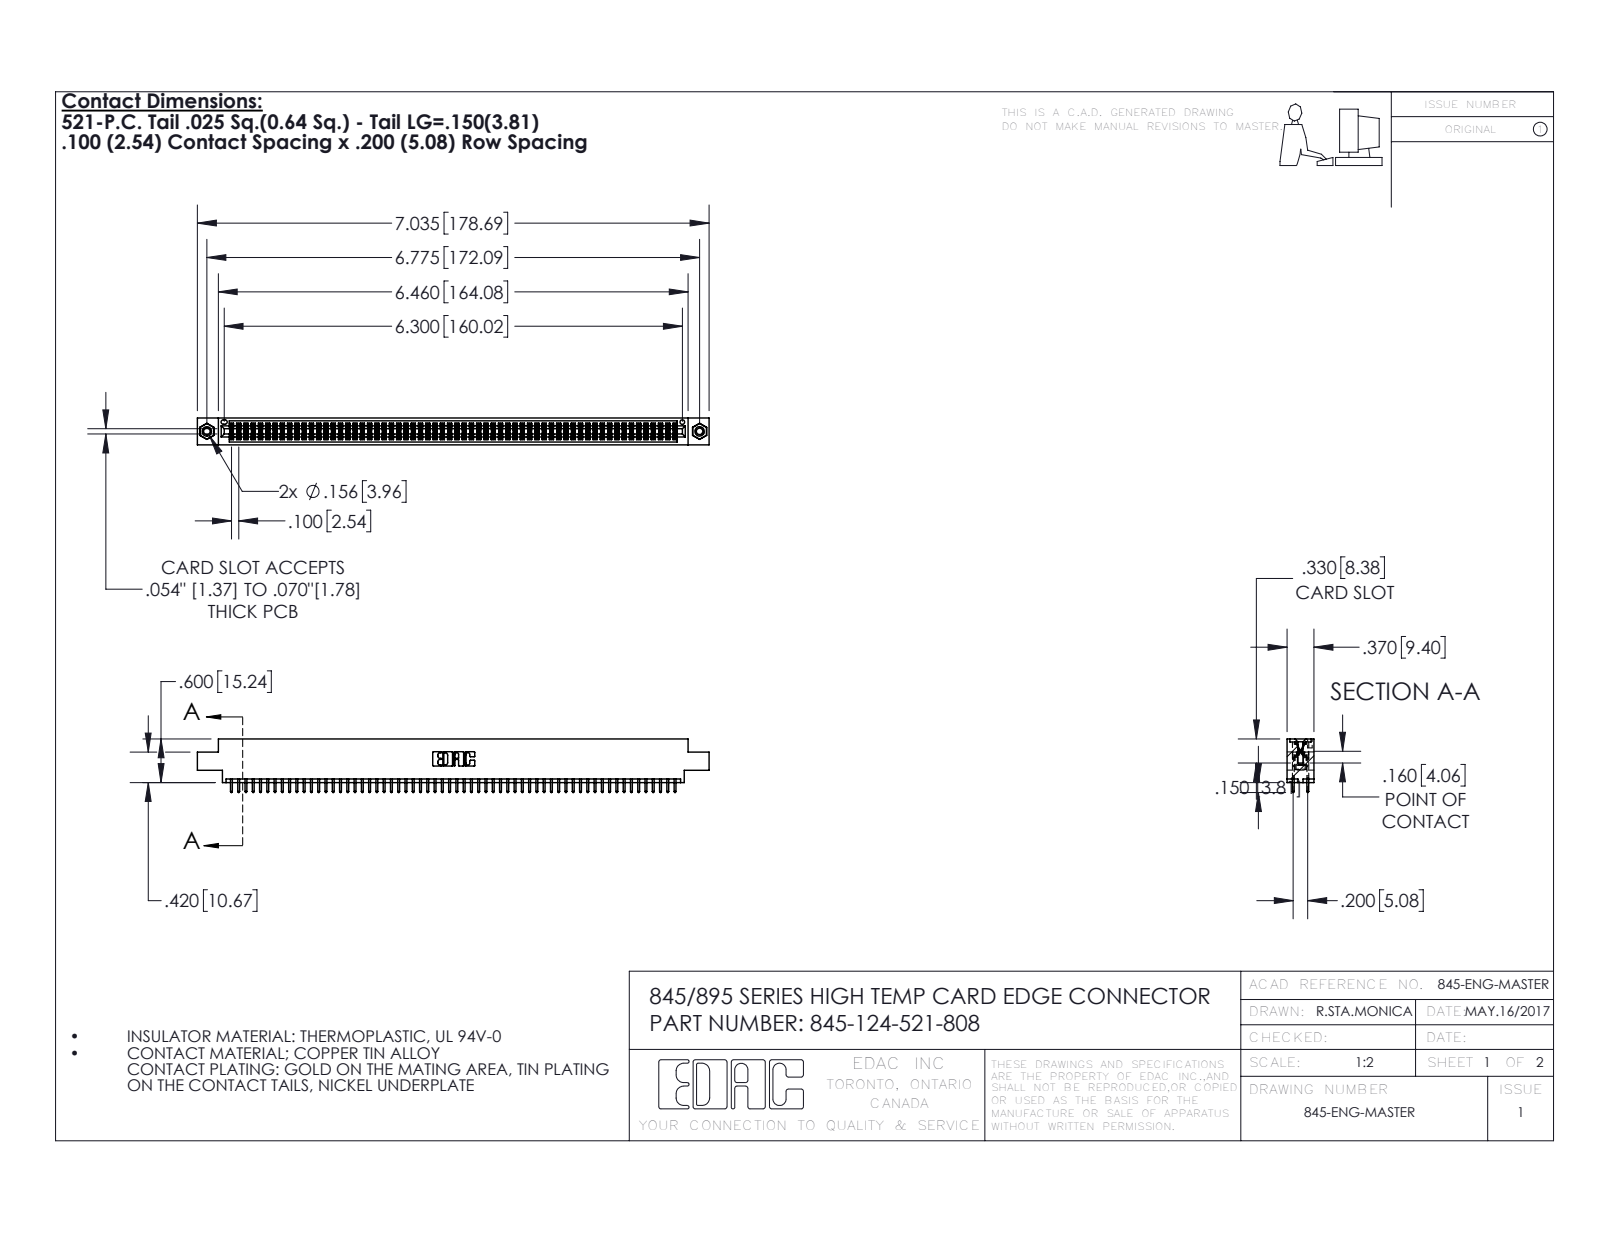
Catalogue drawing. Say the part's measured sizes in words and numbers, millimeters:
The part is named "345-292-001_345-293-121; 345-250-001_345-250-003-102; 845-124-521-808; 845 Part_0.170 Offset - 0.156 Dia-TI". Its 3-D file was written by "SolidWorks 2016 (CONFIG_CONTROL_DESIGN)". It is 127 solids with 6390 faces: 4208 planar, 2166 cylindrical and 16 other. Overall it measures 178.7 by 18.7 by 9.4 millimeters. Its volume is 17 370 cubic millimeters and its surface area 25 900 square millimeters. Round holes: 2 of diameter 2.3, 2 of diameter 3.2, 2 of diameter 4, 1 of diameter 1.6. Round bosses or shafts: 2 of diameter 3.9. Partial cylindrical surfaces (rounded edges, fillets, slot ends): 186 of radius 0.2, 124 of radius 0.3, 22 of radius 0.3, 6 of radius 0.2, 6 of radius 0.8, 3 of radius 0.7, 2 of radius 0.4, 2 of radius 0.5. The main face-to-face distances are 1.8, 7.6, 5.1, 9.4, 2.5, 6.9, 0.6, 5.7, 4.4, 3.8. The hole center spacings are 6.9, 166.1, 172.1.
